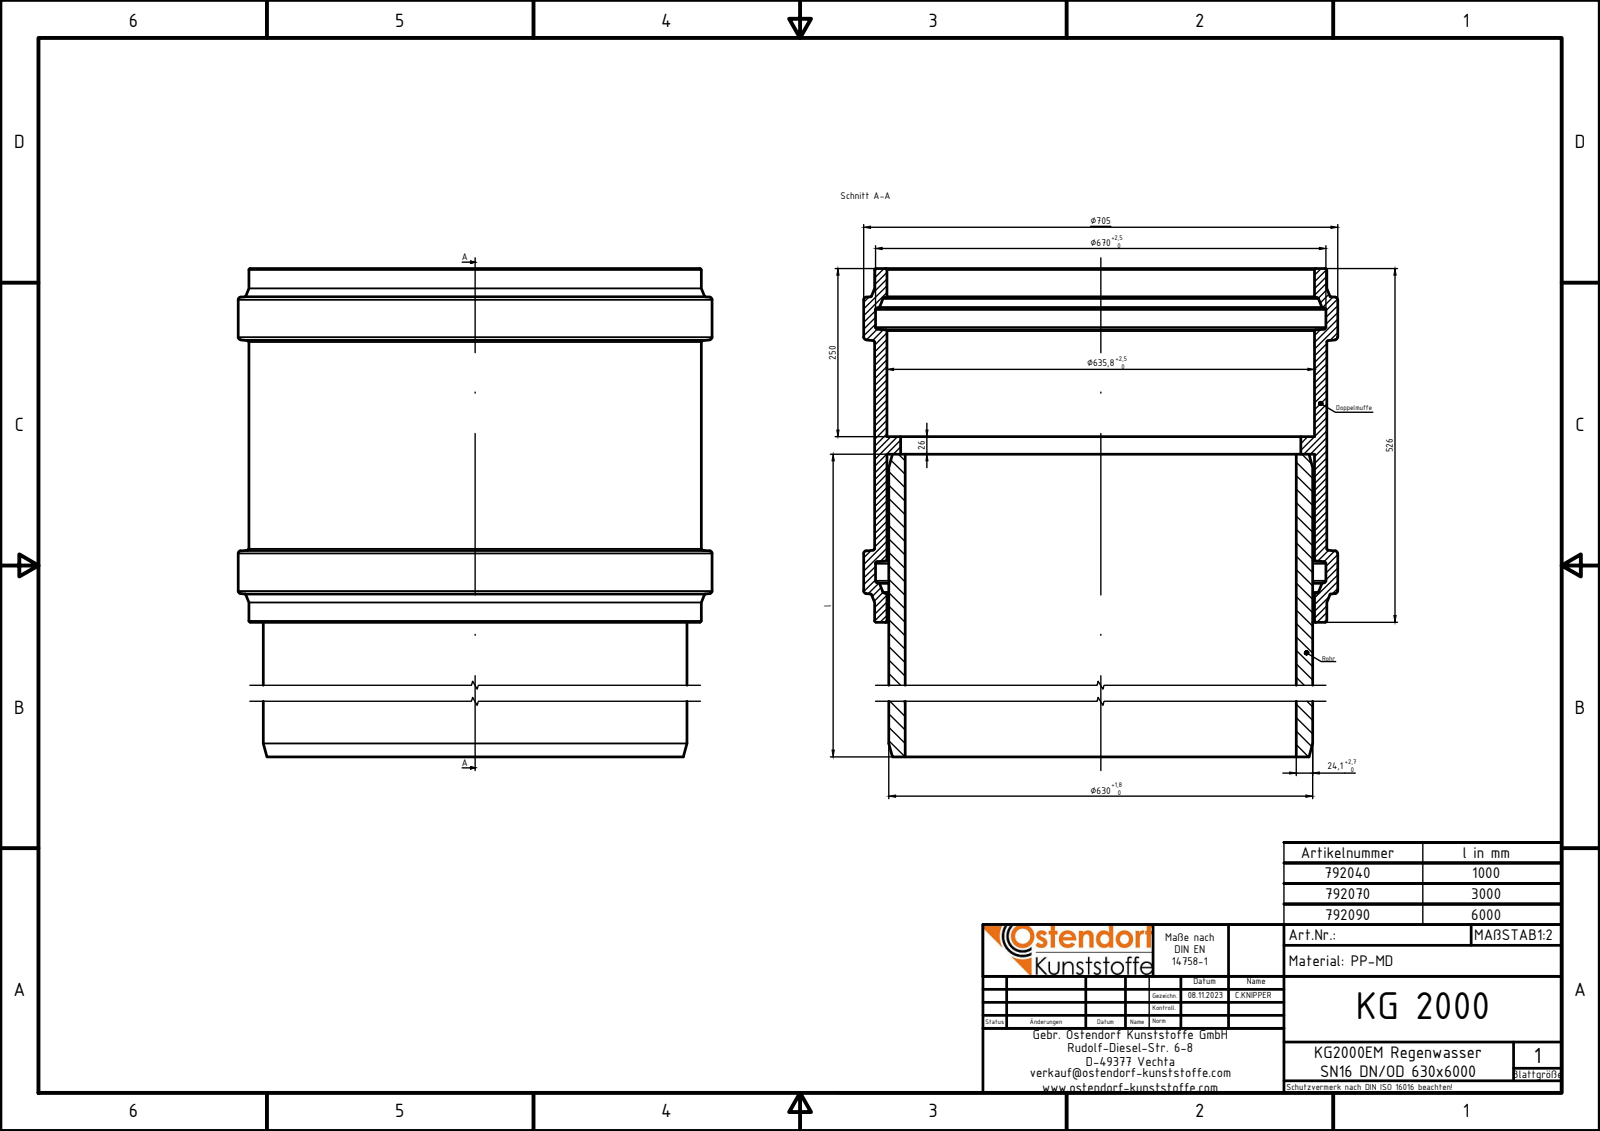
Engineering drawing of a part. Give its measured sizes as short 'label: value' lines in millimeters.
name: 792090z
written by: Autodesk Inventor 2024 (AUTOMOTIVE_DESIGN)
unit: mm
bodies: 1 solid, 60 faces (6 planar, 14 cylindrical, 40 other)
size: 6276 × 704.8 × 704.8
volume: 297 800 000 mm³; area: 25 390 000 mm²
holes: 1× ⌀581.8, 1× ⌀594.8, 1× ⌀635.8, 1× ⌀670
bosses: 1× ⌀704.8, 1× ⌀672.6, 1× ⌀630
face distances: 276, 250, 6026, 5750, 6276, 526, 6000, 26
